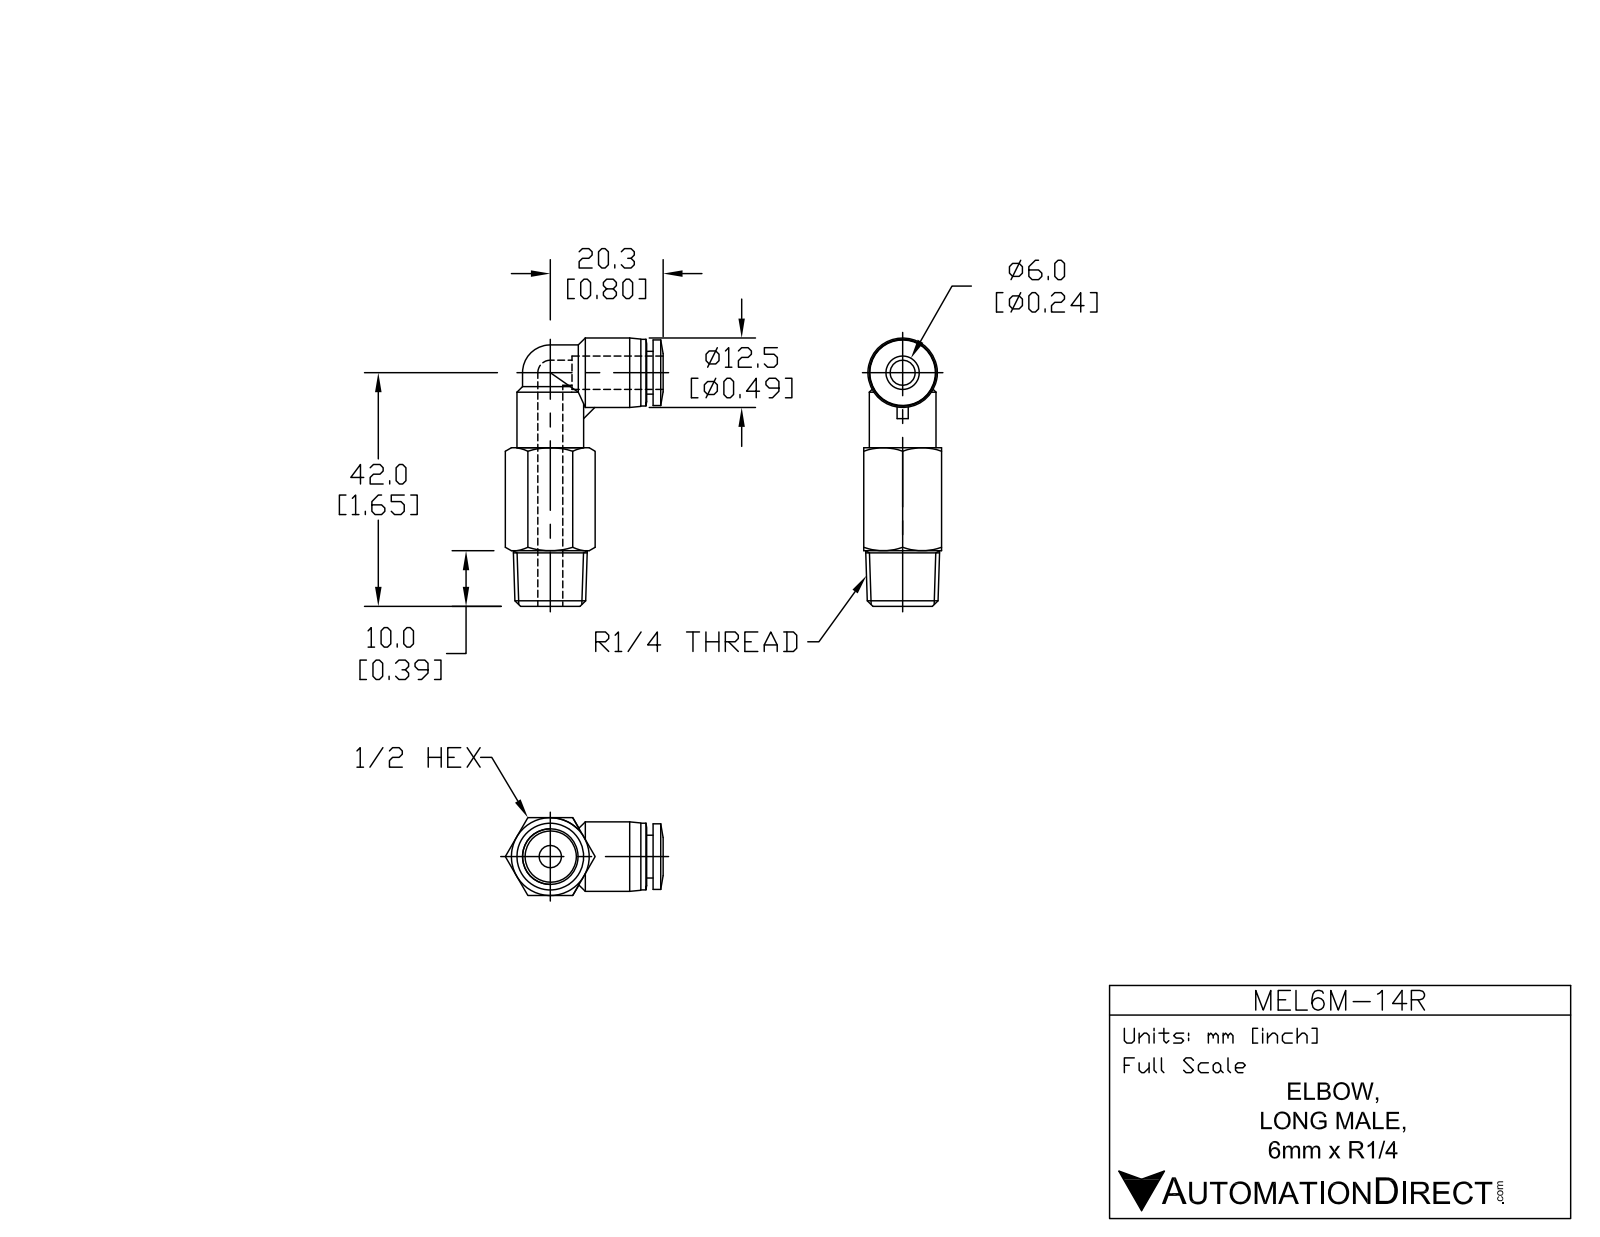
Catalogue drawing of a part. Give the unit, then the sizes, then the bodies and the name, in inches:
Units: inches
Overall size (bounding box): 1.9 × 1.117 × 0.551
Round holes (diameter × count): ⌀0.157 ×2, ⌀0.248 ×1
Round bosses / shafts (diameter × count): ⌀0.472 ×2, ⌀0.492 ×1, ⌀0.465 ×1, ⌀0.303 ×1
Partial cylindrical surfaces — rounded edges, fillets, slot ends (radius × count): R0.197 ×2
Main face-to-face distances: 0.551, 1.122, 0.045, 0.53, 0.575, 0.394, 0.728, 0.236, 0.315, 0.646
Volume: 0.416 in³ · Surface area: 5.863 in²
Bodies: 1 solid, 69 faces (17 planar, 19 cylindrical, 33 other)
Part name (STEP PRODUCT): MEL6M-14R
STEP written by: SolidWorks 2015 (AUTOMOTIVE_DESIGN)
